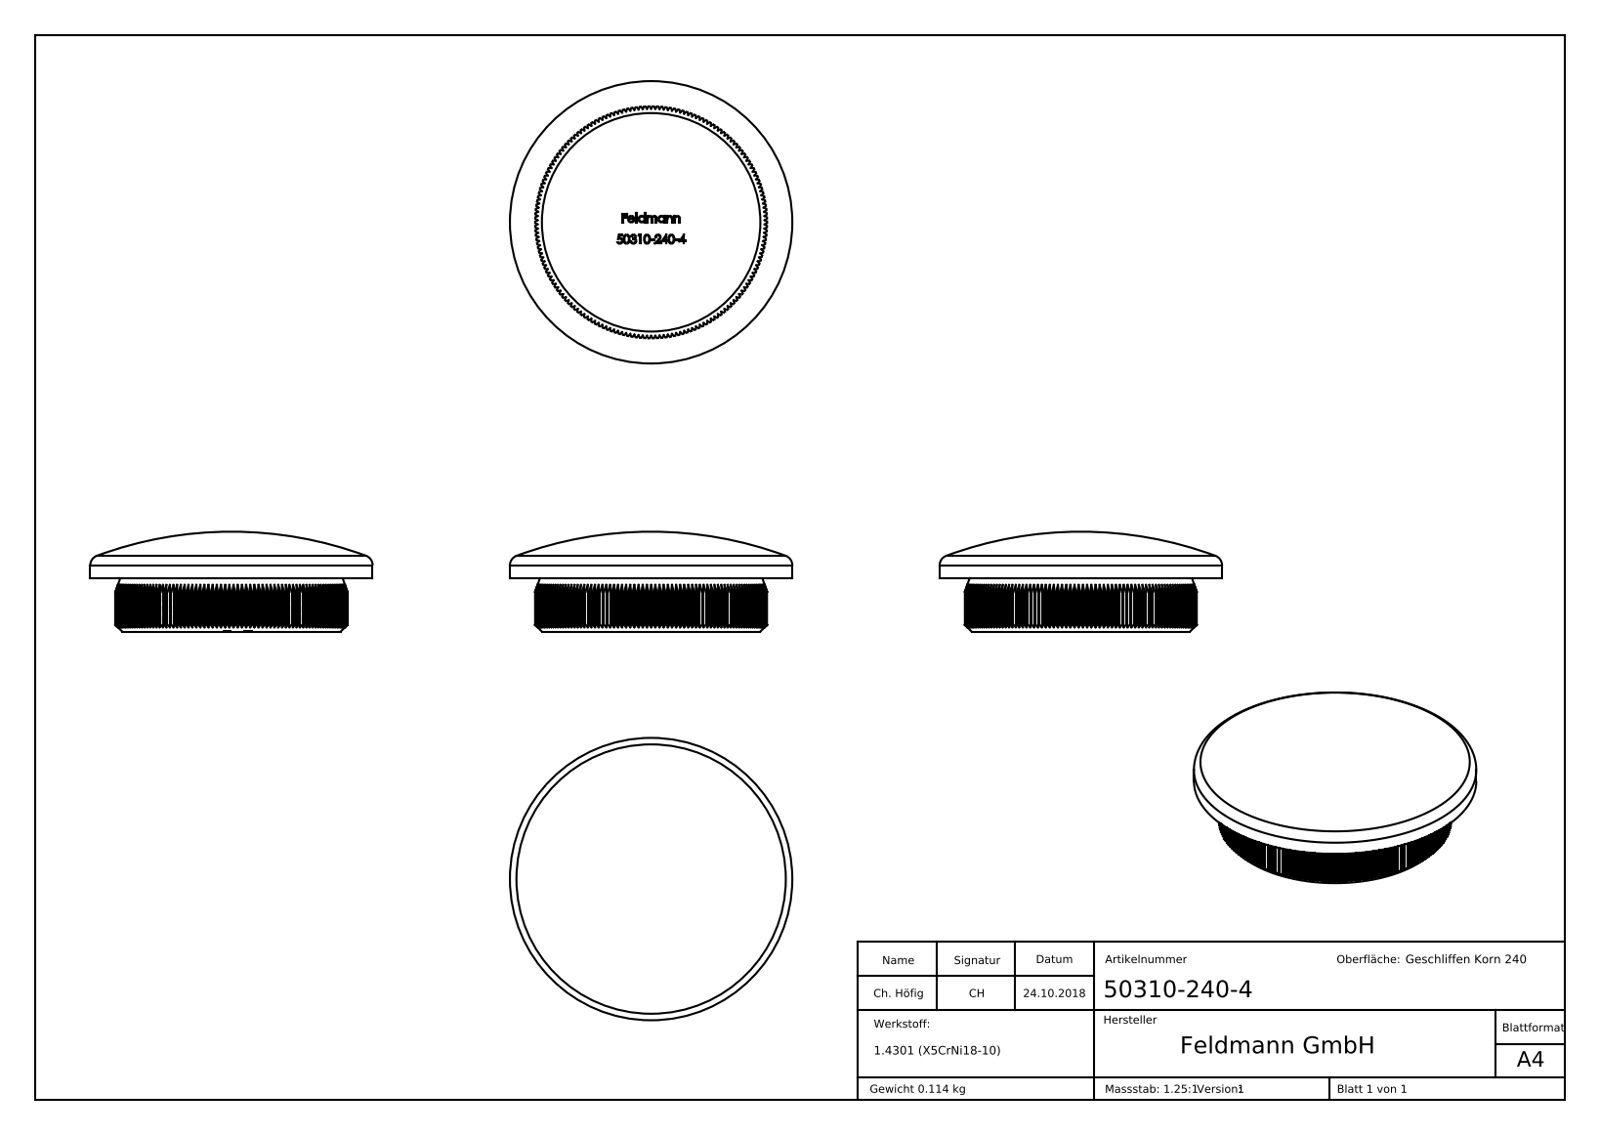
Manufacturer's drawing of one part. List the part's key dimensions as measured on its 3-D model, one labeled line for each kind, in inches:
Part name (STEP PRODUCT): 50310-240-4
STEP written by: SolidWorks 2015 (CONFIG_CONTROL_DESIGN)
Units: inches
Bodies: 1 solid, 744 faces (461 planar, 172 cylindrical, 111 other)
Overall size (bounding box): 1.669 × 1.669 × 0.591
Volume: 0.884 in³ · Surface area: 7.011 in²
Round bosses / shafts (diameter × count): ⌀1.669 ×1
Partial cylindrical surfaces — rounded edges, fillets, slot ends (radius × count): R0.685 ×1
Main face-to-face distances: 0.315, 0.672, 0.671, 0.311, 0.672, 0.117, 0.015, 0.055, 0.133, 0.126
